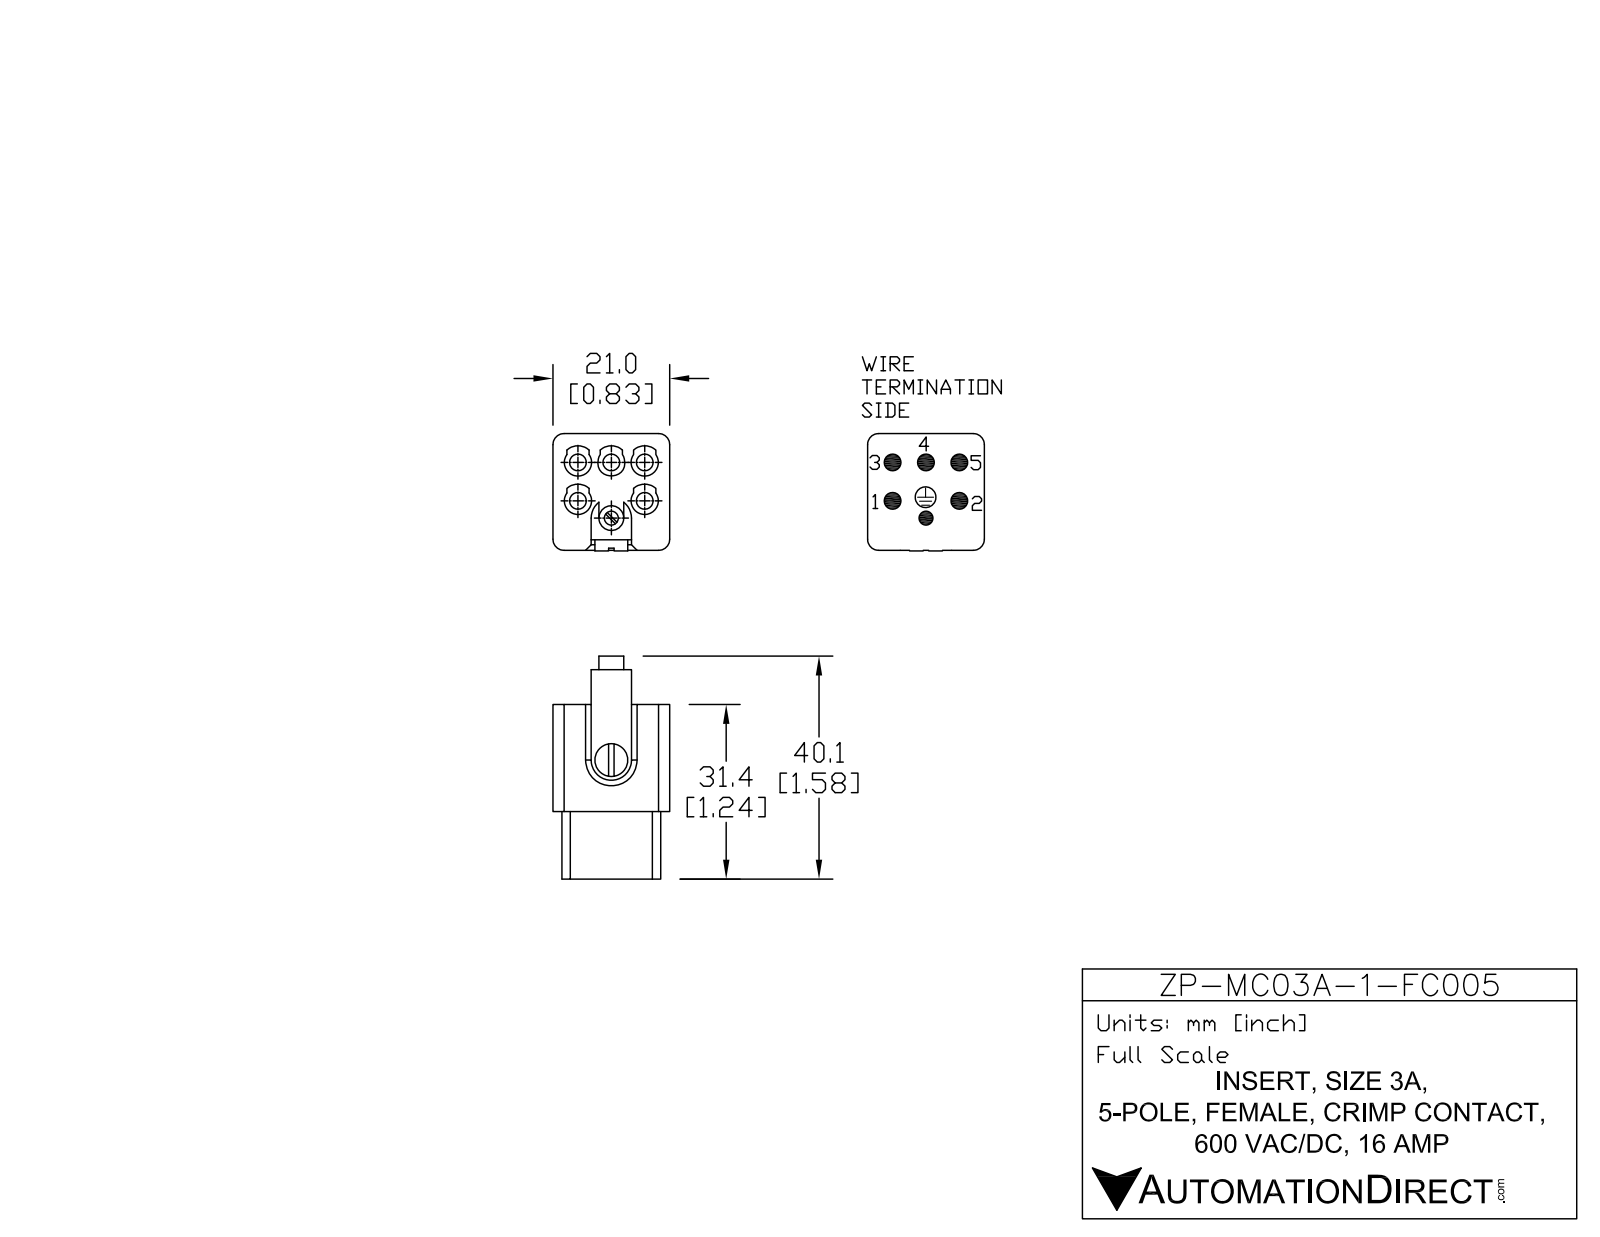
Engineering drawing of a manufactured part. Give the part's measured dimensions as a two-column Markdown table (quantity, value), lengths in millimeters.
| quantity | value |
| --- | --- |
| part name | ZP-3A-5-FC-INSERT |
| STEP written by | SolidWorks 2011 (AUTOMOTIVE_DESIGN) |
| units | millimeters |
| bodies | 1 solid, 76 faces (46 planar, 29 cylindrical, 1 other) |
| overall size | 40.1 × 21.11 × 21 |
| volume | 9 561 mm³ |
| surface area | 5 949 mm² |
| round holes (diameter × count) | 3 × 5, 2.5 × 1 |
| round bosses / shafts (diameter × count) | 5.9 × 1, 4.45 × 1 |
| partial cylindrical surfaces (radius × count) | 2.45 × 5, 3.01 × 5, 1.5 × 4, 2 × 4, 3.62 × 2 |
| main face-to-face distances | 21, 1.62, 19.38, 2, 19, 31.4, 17.76, 19.25, 12.15, 19.11 |
| hole center spacings | 6, 6.75, 6.9, 9.14, 11.66, 12, 13.84, 10 |
